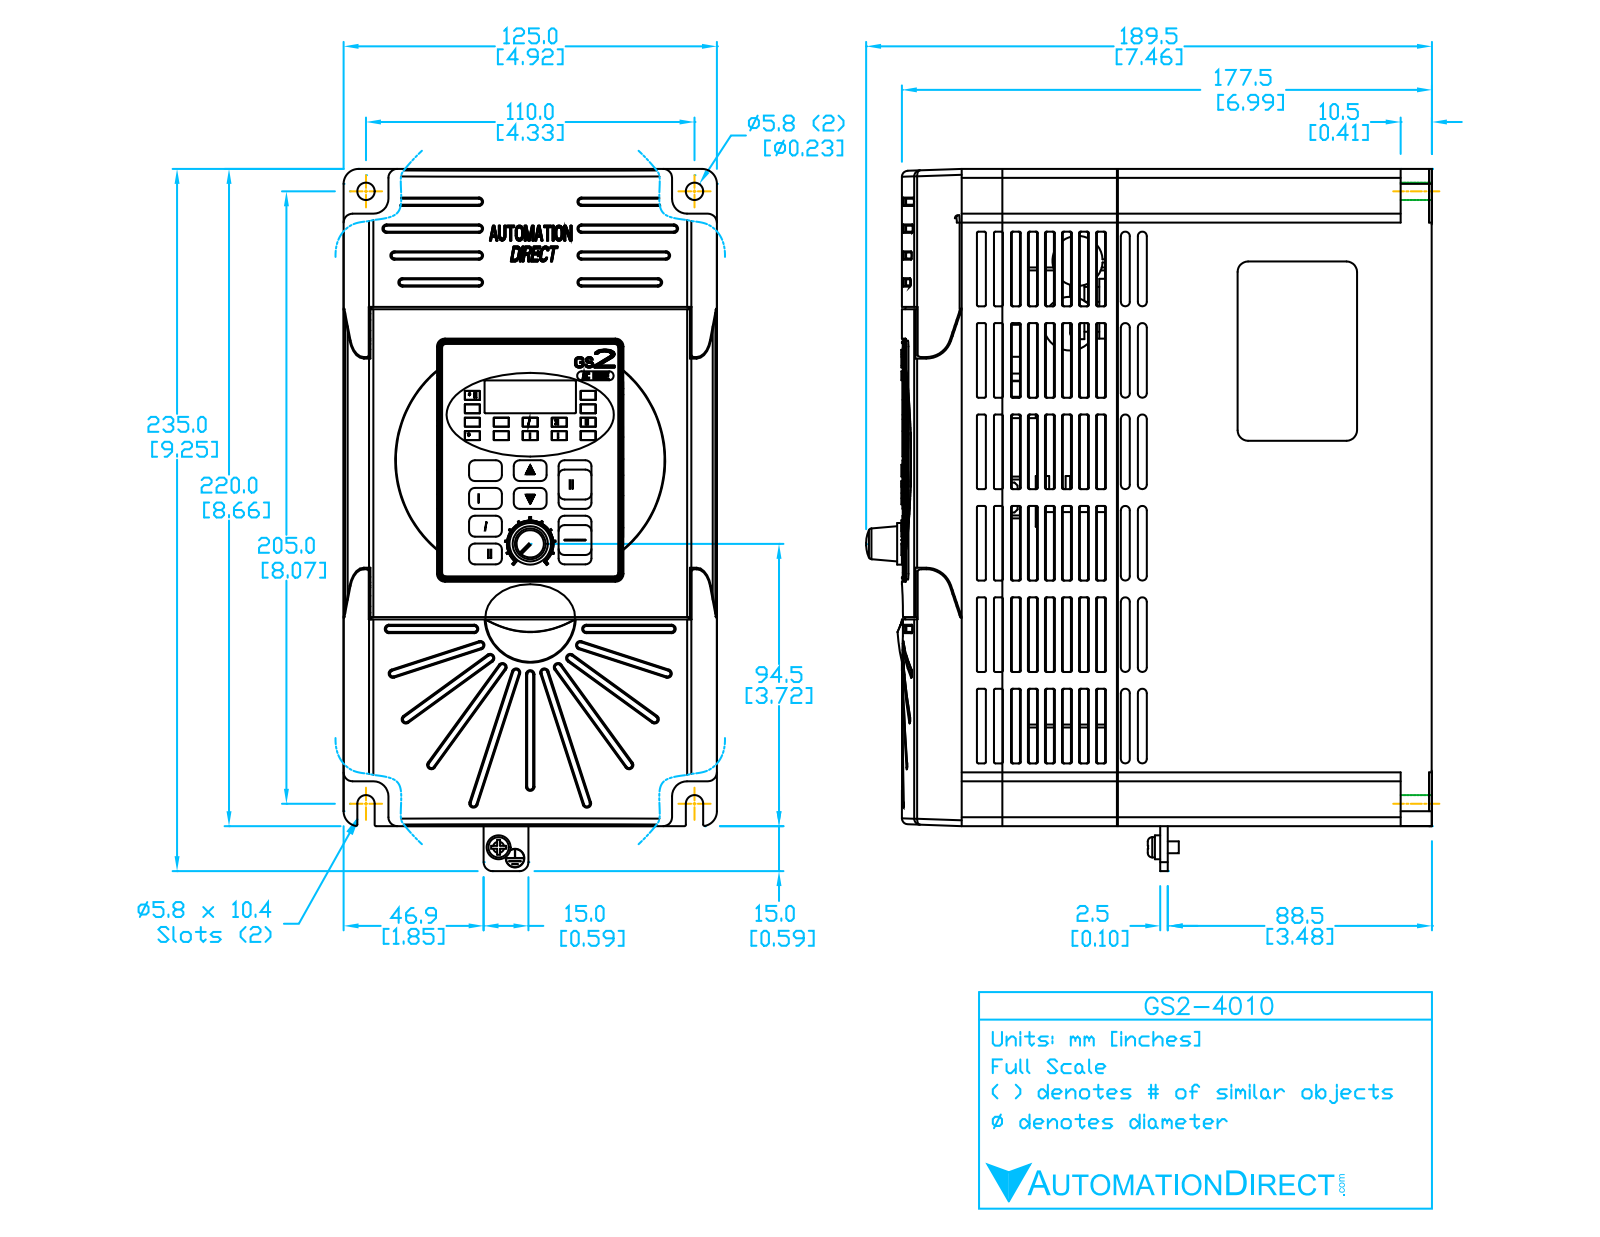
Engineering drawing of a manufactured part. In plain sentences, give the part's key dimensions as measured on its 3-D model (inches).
The part is named "GS2-4010". Its 3-D file was written by "SolidWorks 2013 (AUTOMOTIVE_DESIGN)". It is 1 solid with 795 faces: 358 planar, 218 cylindrical and 219 other. Overall it measures 9.25 by 7.485 by 4.92 inches. Its volume is 282.9 cubic inches and its surface area 350.8 square inches. Round holes: 2 of diameter 0.23, 1 of diameter 3.2. Round bosses or shafts: 1 of diameter 0.545, 1 of diameter 0.258, 1 of diameter 0.15. Partial cylindrical surfaces (rounded edges, fillets, slot ends): 40 of radius 0.06, 38 of radius 0.04, 12 of radius 0.125, 8 of radius 0.2, 6 of radius 0.019, 6 of radius 0.064, 6 of radius 0.25, 4 of radius 0.1. The main face-to-face distances are 0.015, 4.905, 4.92, 6.181, 8.645, 4.89, 8.66, 6.17, 0.58, 0.565. The hole center spacings are 4.33.
